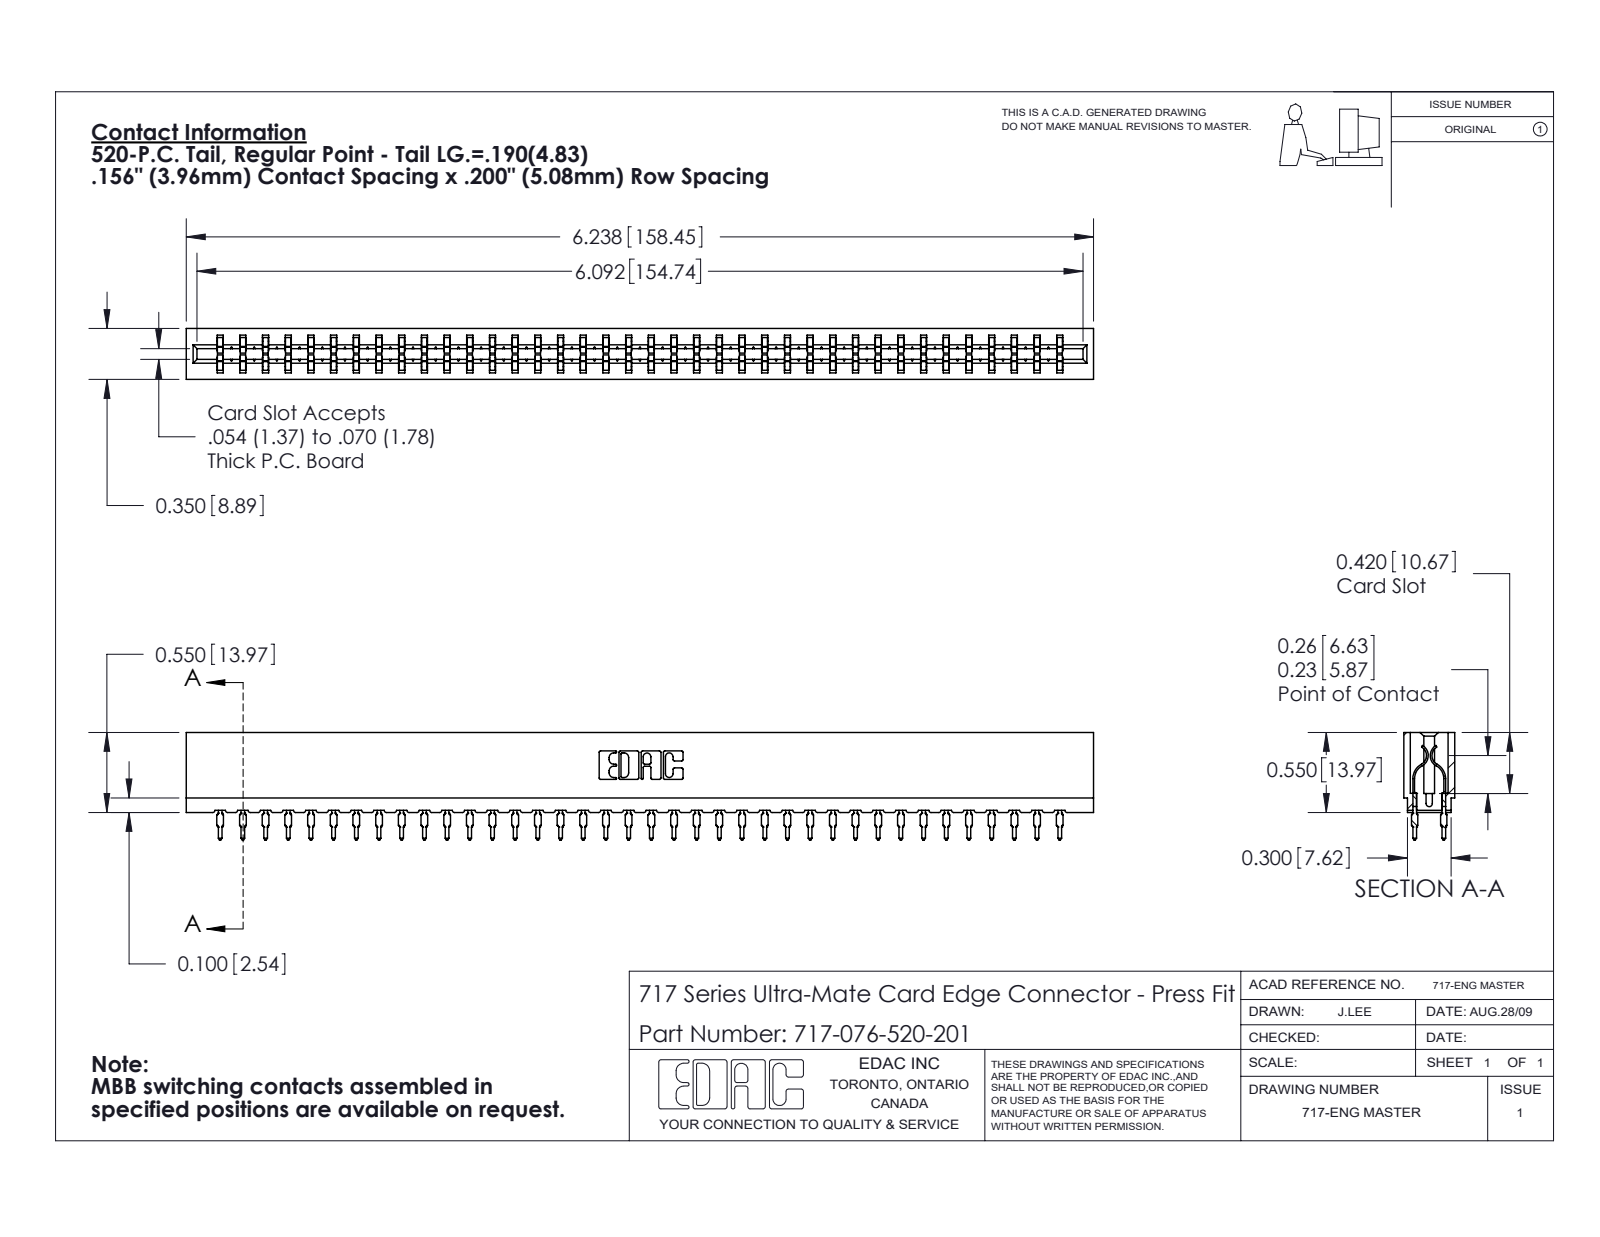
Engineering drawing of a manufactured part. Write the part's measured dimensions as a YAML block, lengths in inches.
part_name: "717 Part_Insulator Option - 06; 717-076-520-201; 745-292-001_520"
step_written_by: "SolidWorks 2020 (CONFIG_CONTROL_DESIGN)"
units: inches
bodies: {solids: 77, faces: 6934, planar: 3588, cylindrical: 1370, other: 1976}
overall_size: [6.238, 0.739, 0.35]
volume: 0.835
surface_area: 31.76
partial_cylinders:
  - {radius: 0.021, count: 152}
  - {radius: 0.015, count: 76}
  - {radius: 0.01, count: 22}
  - {radius: 0.005, count: 8}
  - {radius: 0.011, count: 8}
  - {radius: 0.007, count: 6}
  - {radius: 0.031, count: 6}
  - {radius: 0.026, count: 3}
face_to_face_distances: [0.212, 0.138, 0.35, 0.063, 0.287, 0.076, 0.149, 0.074, 0.045, 0.305]
